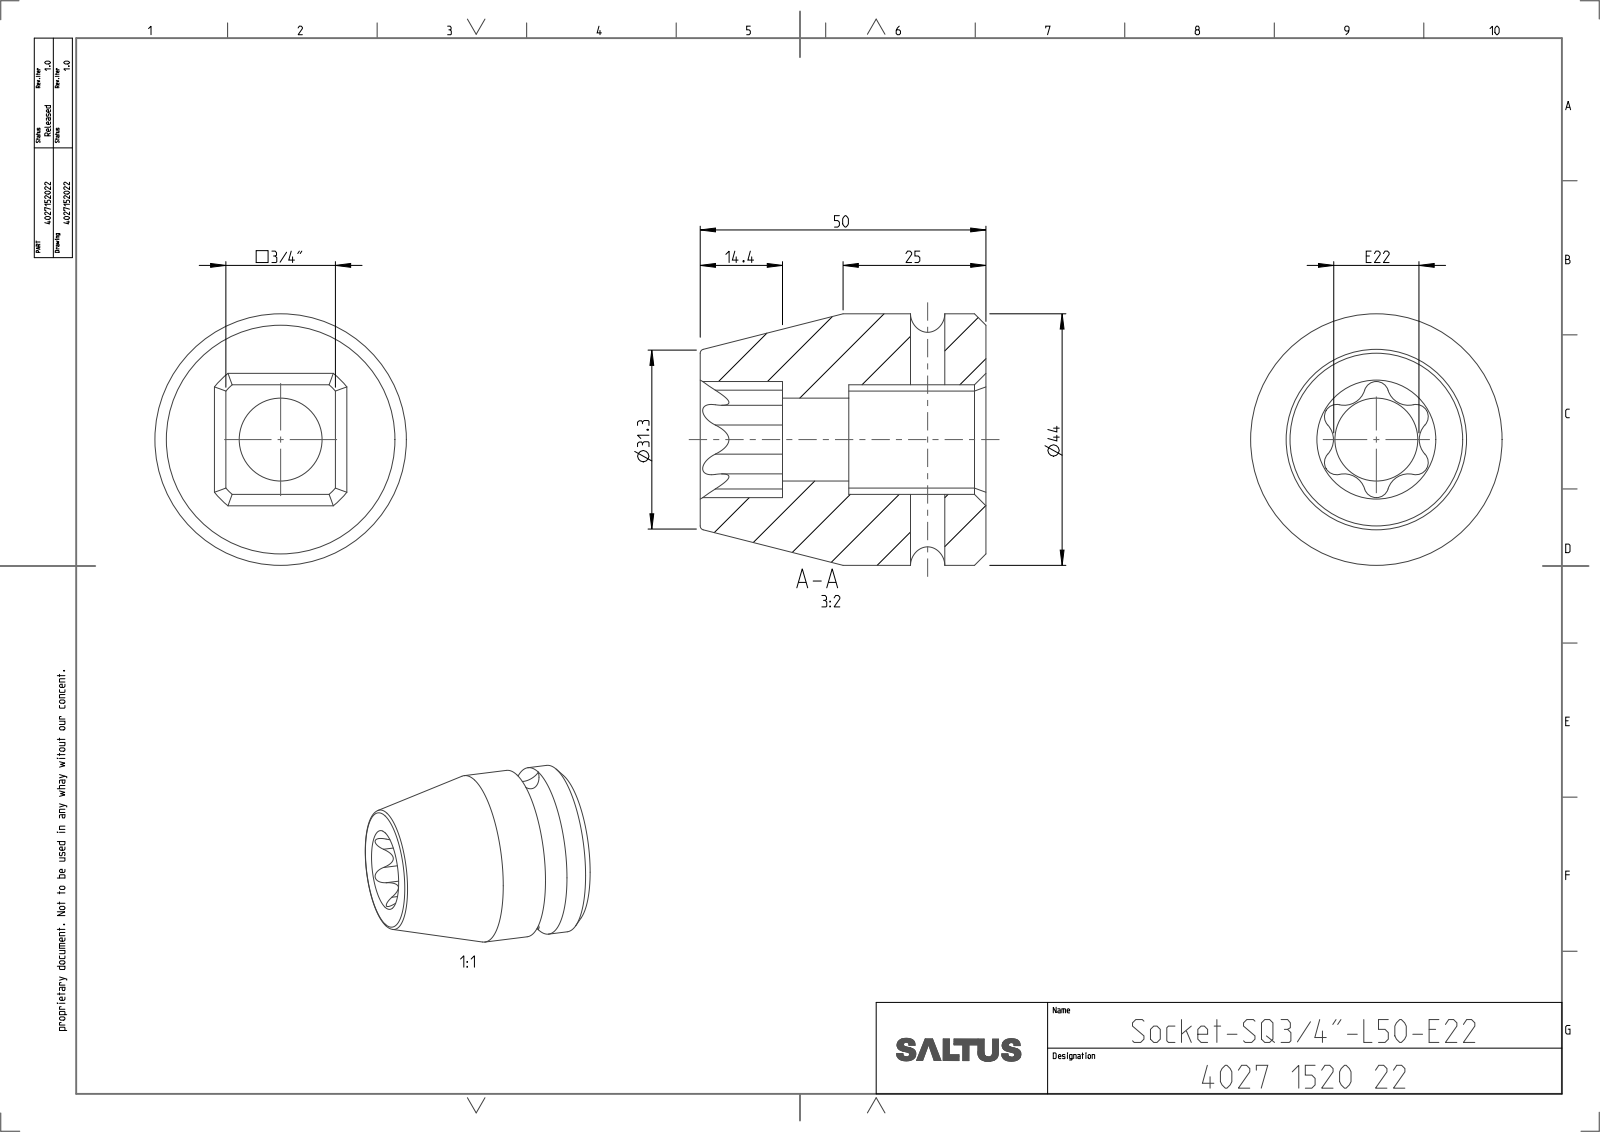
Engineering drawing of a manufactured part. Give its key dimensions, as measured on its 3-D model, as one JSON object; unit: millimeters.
{"part_name": "4027152022", "step_written_by": "CREO PARAMETRIC BY PTC INC, 2022414 (CONFIG_CONTROL_DESIGN)", "units": "millimeters", "bodies": {"solids": 1, "faces": 52, "planar": 12, "cylindrical": 26, "other": 14}, "overall_size": [50, 44, 44], "volume_mm3": 48931, "surface_area_mm2": 12005, "round_holes": [[6, 1], [14.5, 1]], "round_bosses_or_shafts": [[44, 1]], "partial_cylinders_radius": [[2.14, 6], [3.74, 6], [12.8, 1]], "face_to_face_distances": [19.18, 50, 24, 26, 35.6, 11.6, 14.4]}
